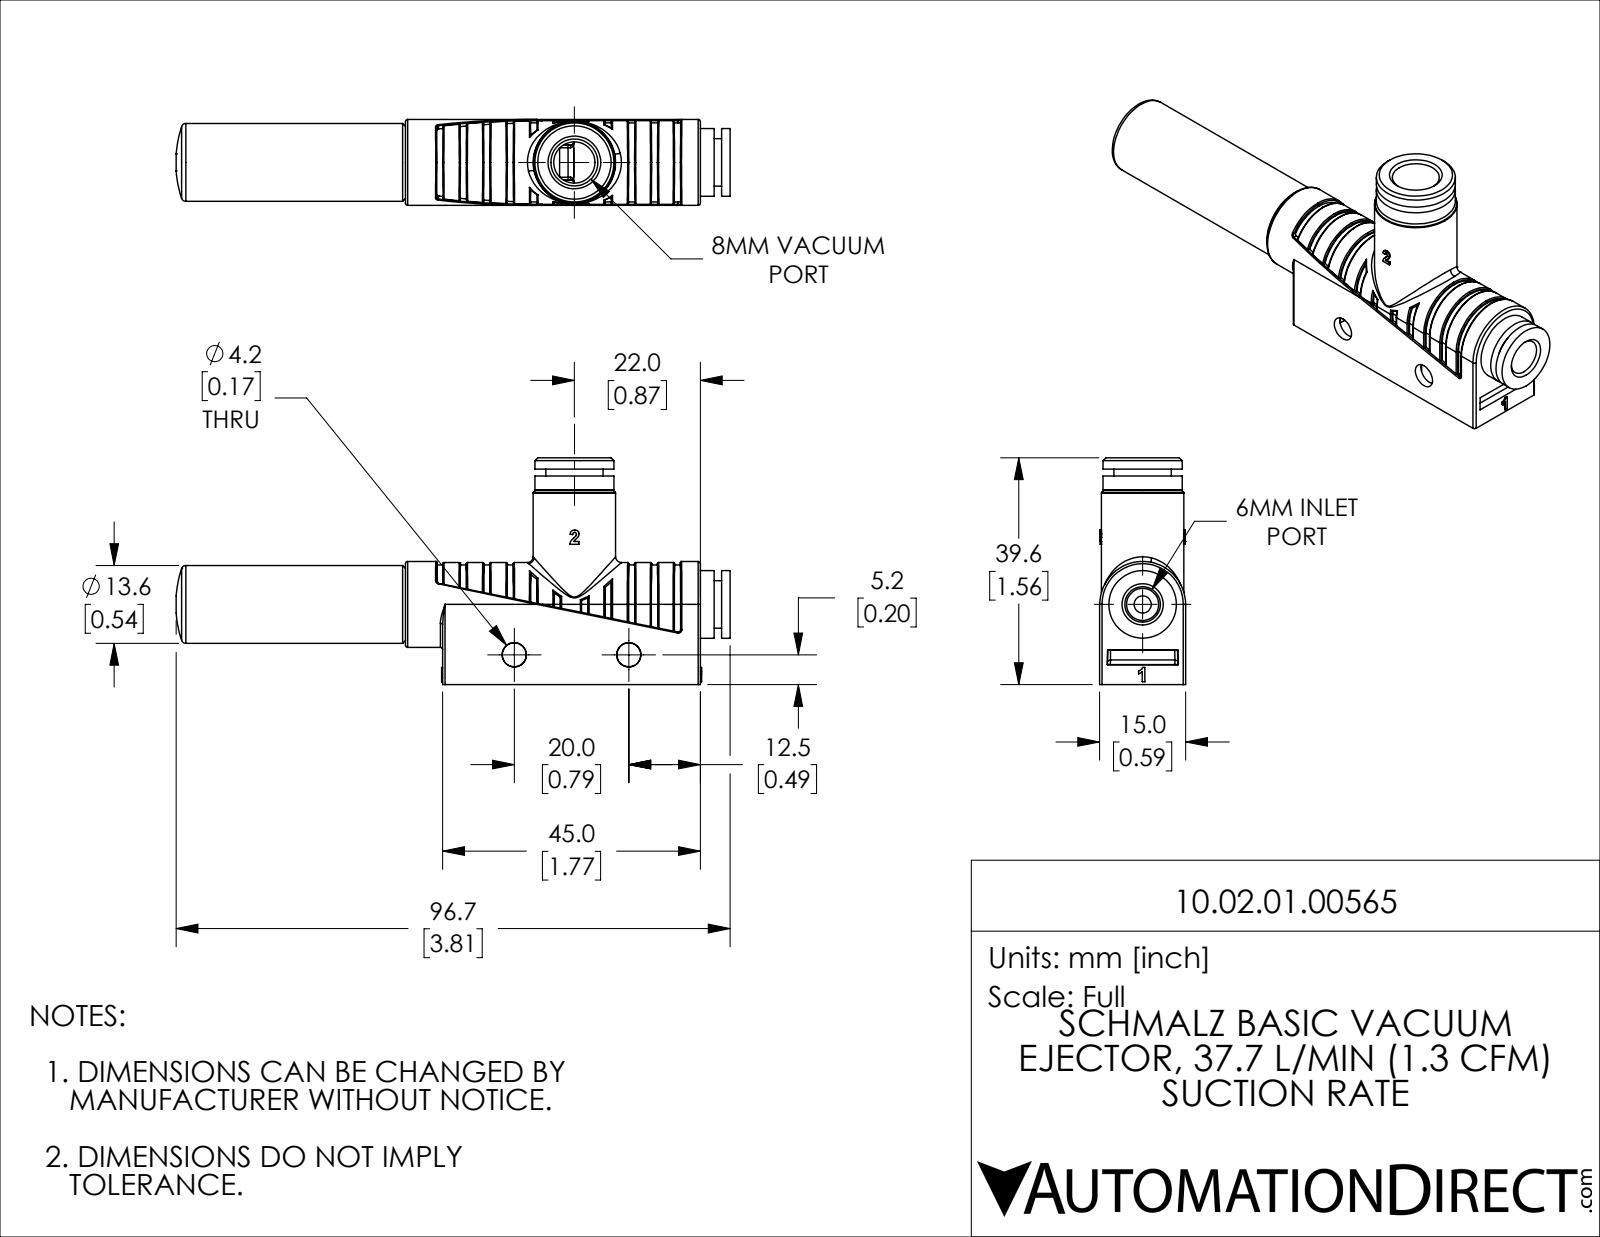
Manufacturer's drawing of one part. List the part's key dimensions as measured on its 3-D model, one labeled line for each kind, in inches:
Part name (STEP PRODUCT): 10.02.01.00565
STEP written by: SolidWorks 2021 (CONFIG_CONTROL_DESIGN)
Units: inches
Bodies: 5 solids, 518 faces (196 planar, 120 cylindrical, 202 other)
Overall size (bounding box): 3.809 × 1.559 × 0.591
Volume: 0.845 in³ · Surface area: 19.54 in²
Round holes (diameter × count): ⌀0.118 ×1, ⌀0.24 ×1, ⌀0.244 ×1, ⌀0.276 ×1, ⌀0.299 ×1, ⌀0.323 ×1, ⌀0.331 ×1, ⌀0.337 ×1, ⌀0.362 ×1, ⌀0.383 ×1, ⌀0.39 ×1, ⌀0.469 ×1
Round bosses / shafts (diameter × count): ⌀0.591 ×1, ⌀0.567 ×1, ⌀0.543 ×1, ⌀0.535 ×1, ⌀0.465 ×1, ⌀0.394 ×1, ⌀0.327 ×1
Partial cylindrical surfaces — rounded edges, fillets, slot ends (radius × count): R0.008 ×26, R0.016 ×12, R0.02 ×2, R0.039 ×1, R0.083 ×1, R0.244 ×1, R0.269 ×1, R0.272 ×1
Main face-to-face distances: 0.591, 0.547, 1.028, 0.205, 0.094, 1.976, 0.242, 0.789, 0.786, 0.239
